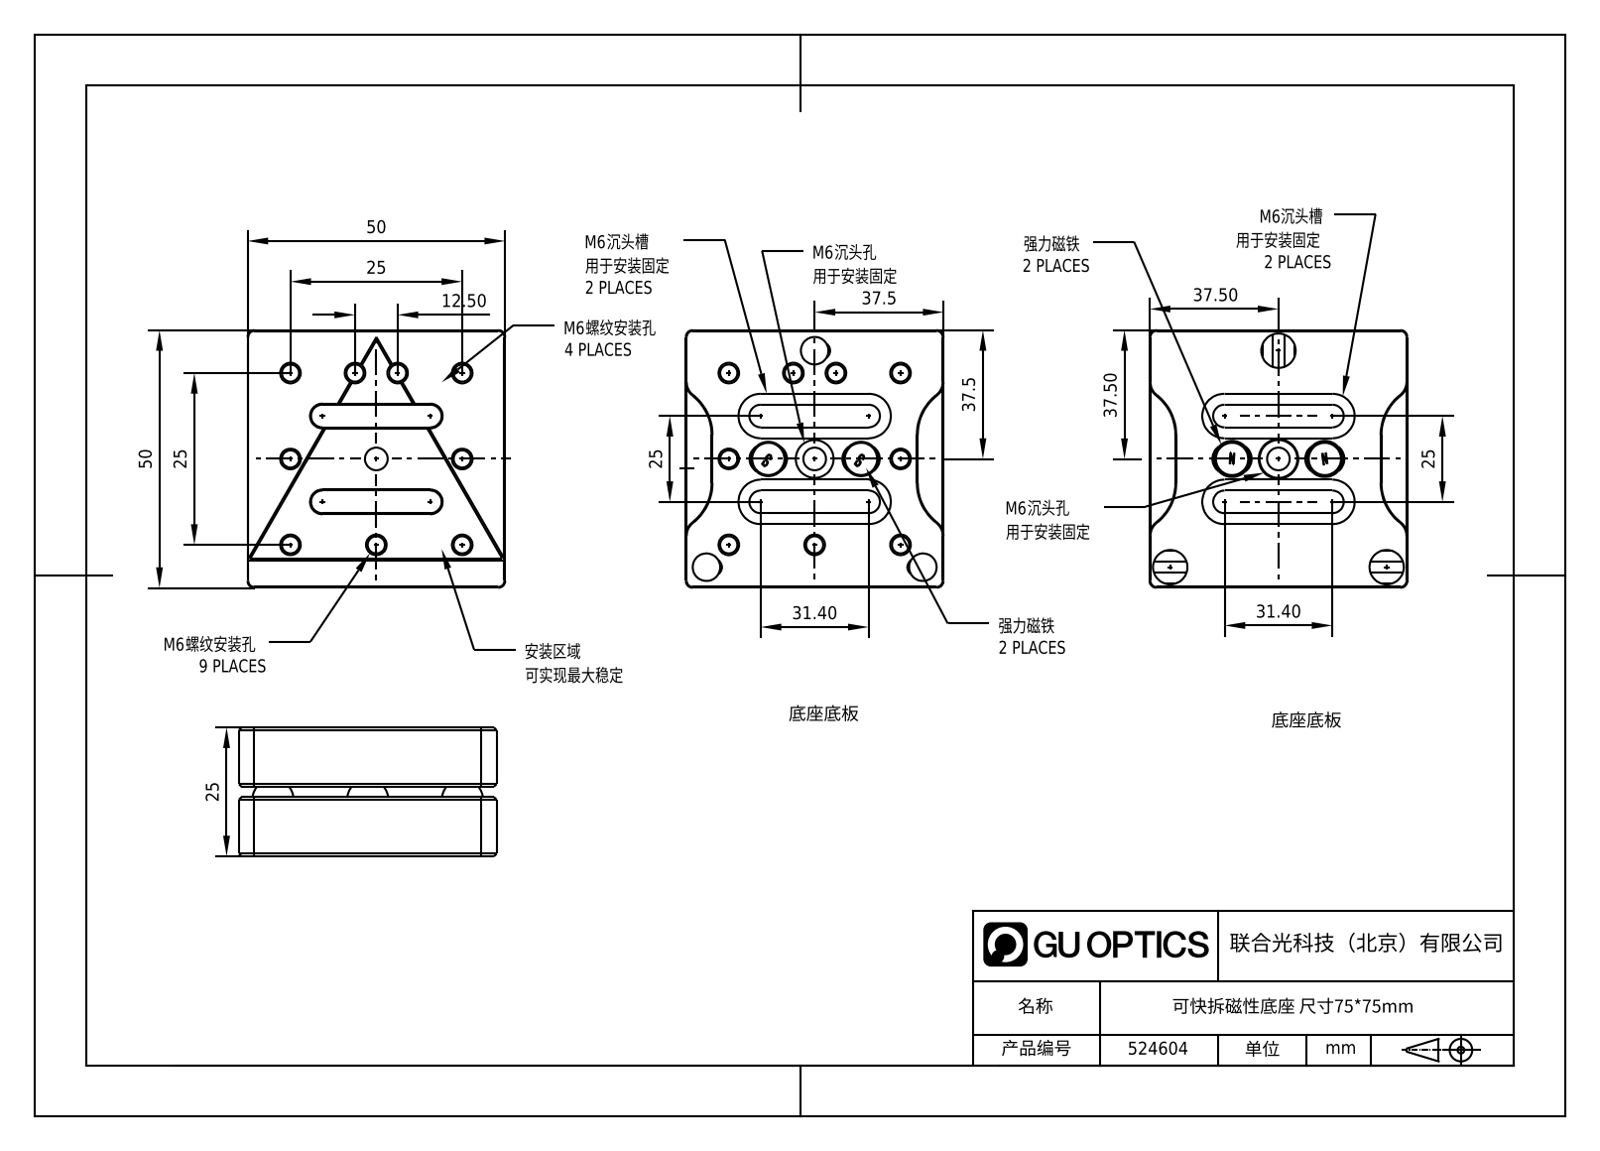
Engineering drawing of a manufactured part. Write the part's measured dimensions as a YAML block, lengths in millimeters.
part_name: "1.4.6.42_ZGD-K75_可调光学接杆底座，尺寸75mmx75mm，带M6安装孔"
step_written_by: "SolidWorks 2018 (CONFIG_CONTROL_DESIGN)"
units: millimeters
bodies: {solids: 0, faces: 247, planar: 91, cylindrical: 90, other: 66}
overall_size: [75, 75, 24.99]
round_holes:
  - {diameter: 5, count: 9}
  - {diameter: 3, count: 4}
  - {diameter: 6.6, count: 1}
round_bosses_or_shafts:
  - {diameter: 3, count: 1}
partial_cylinders:
  - {radius: 2, count: 4}
  - {radius: 3.3, count: 4}
  - {radius: 5, count: 4}
  - {radius: 6.47, count: 4}
  - {radius: 14.5, count: 4}
face_to_face_distances: [12.99, 12, 24.99, 0.99, 75, 6, 25, 3.17, 9.77, 18.99]
hole_center_spacings: [25, 35.36, 55.9, 50, 18.8, 25.76, 31.2, 31.28]
